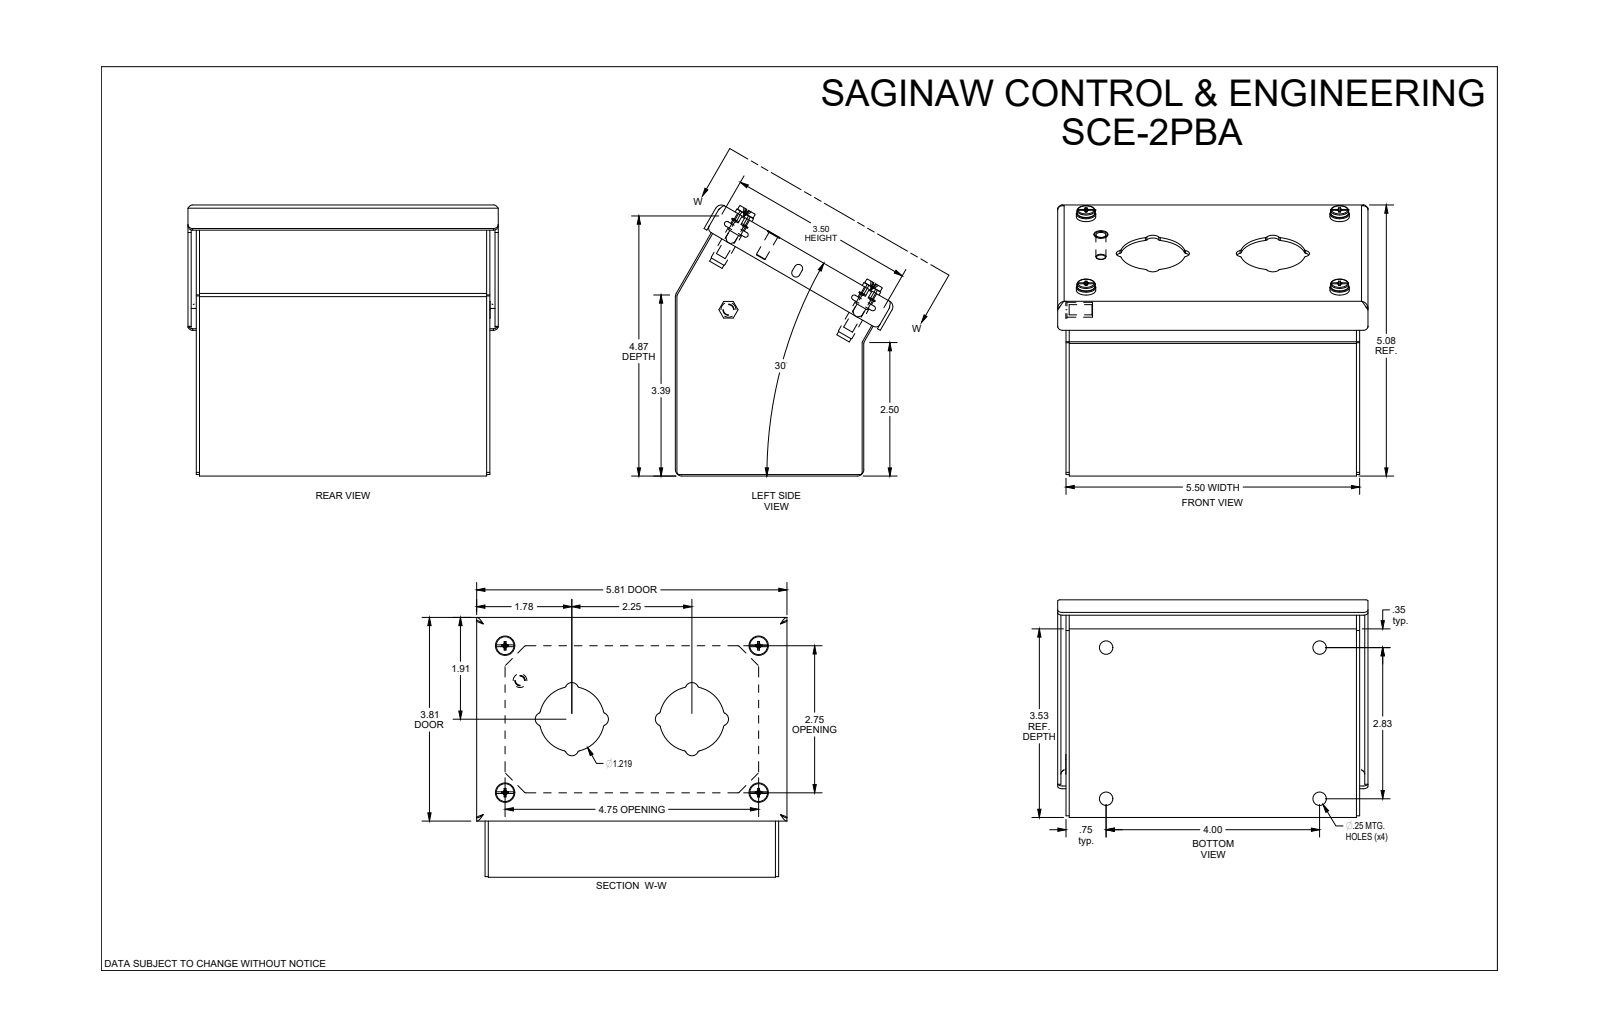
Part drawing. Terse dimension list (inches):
name: SCE-2PBA
written by: SolidWorks 2021 (AUTOMOTIVE_DESIGN)
unit: in
bodies: 19 solids, 628 faces (240 planar, 216 cylindrical, 172 other)
size: 5.812 × 5.098 × 4.097
volume: 8.168 in³; area: 278 in²
holes: 8× ⌀0.25, 5× ⌀0.19, 4× ⌀0.22, 4× ⌀0.266, 4× ⌀0.317
bosses: 5× ⌀0.188, 4× ⌀0.362, 4× ⌀0.34, 4× ⌀0.334, 4× ⌀0.292, 4× ⌀0.27, 4× ⌀0.26, 4× ⌀0.146
rounds: 20× R0.04, 20× R0.06, 12× R0.03, 10× R0.01, 8× R0.115, 8× R0.125, 8× R0.24, 6× R0.12
face distances: 0.06, 5.44, 0.06, 5.38, 5.5, 3.47, 0.156, 3.47, 3.41, 3.53
hole spacings: 4.75, 2.75, 2.753, 2.83, 4, 4.9, 5.489, 5.49
